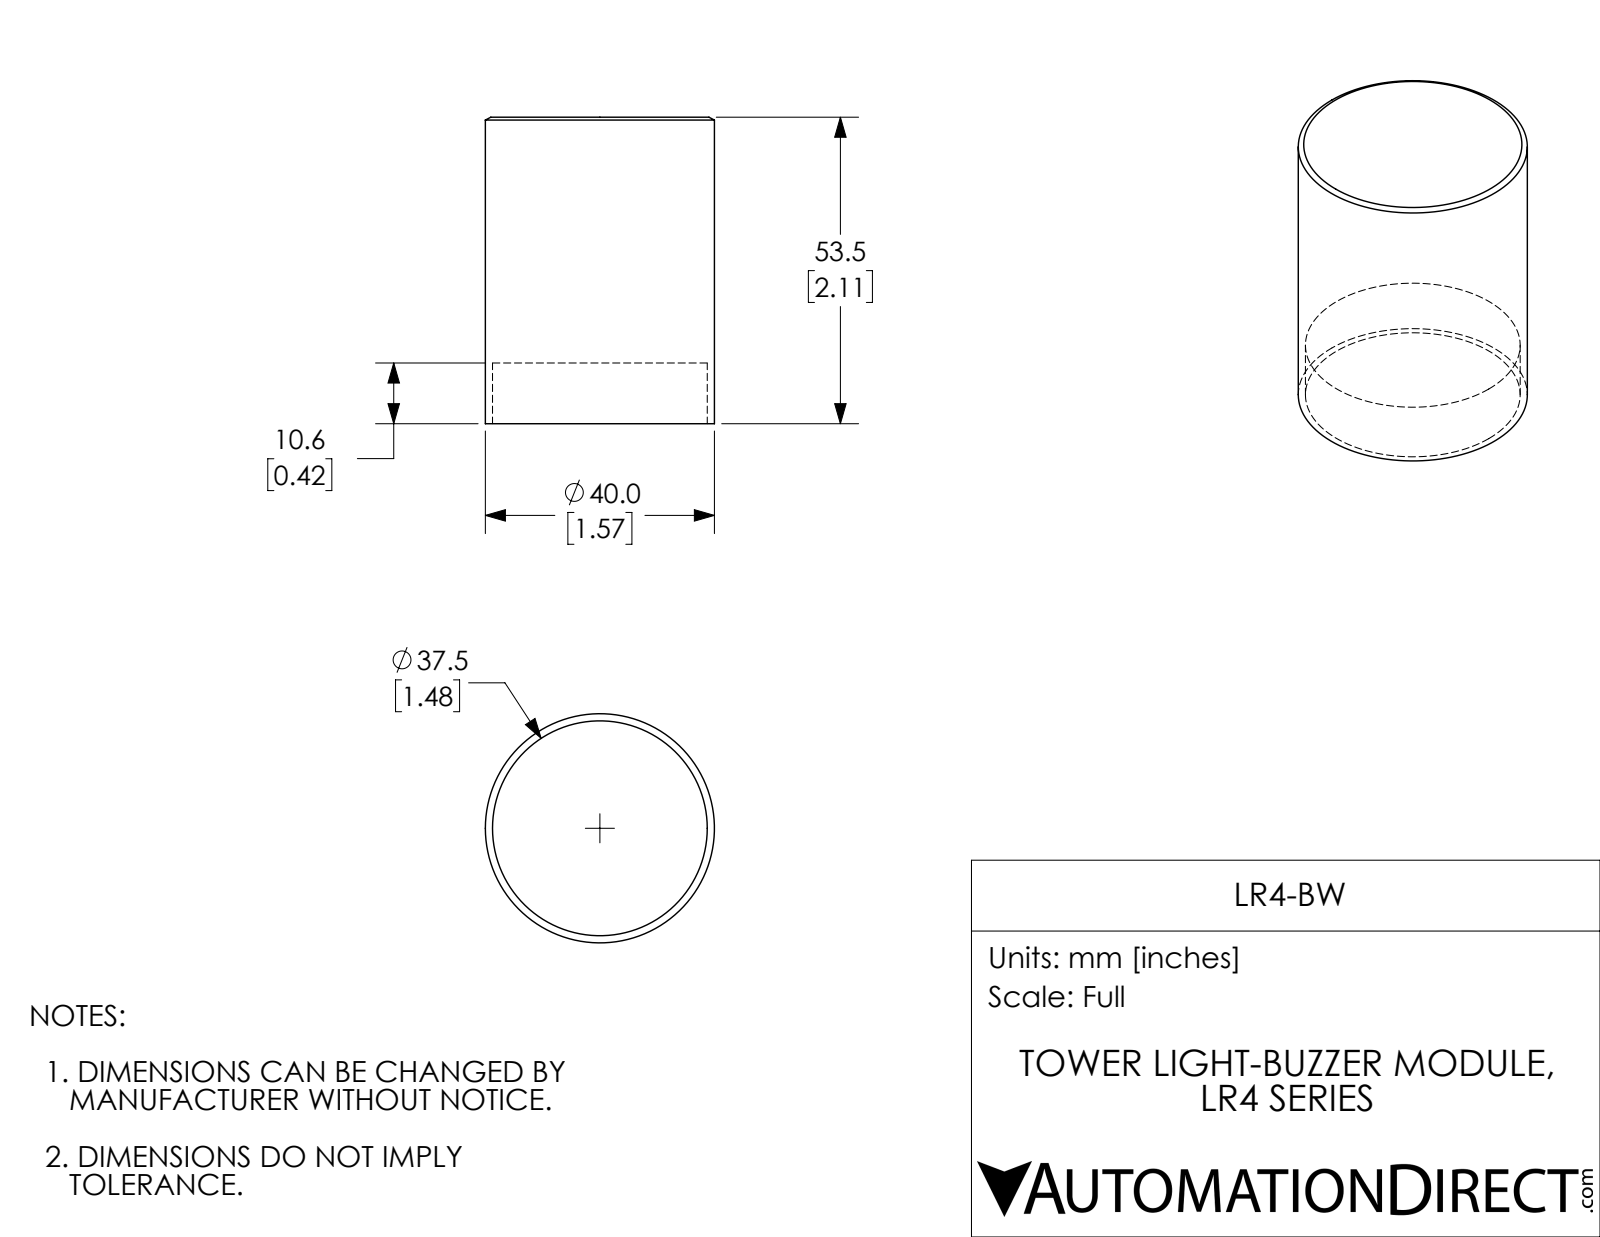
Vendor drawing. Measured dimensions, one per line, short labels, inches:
name: LR4-BW
written by: SolidWorks 2017 (AUTOMOTIVE_DESIGN)
unit: in
bodies: 1 solid, 9 faces (3 planar, 4 cylindrical, 2 other)
size: 2.106 × 1.575 × 1.575
volume: 3.386 in³; area: 16.18 in²
holes: 1× ⌀1.476
bosses: 1× ⌀1.575
face distances: 1.689, 0.417, 2.106
